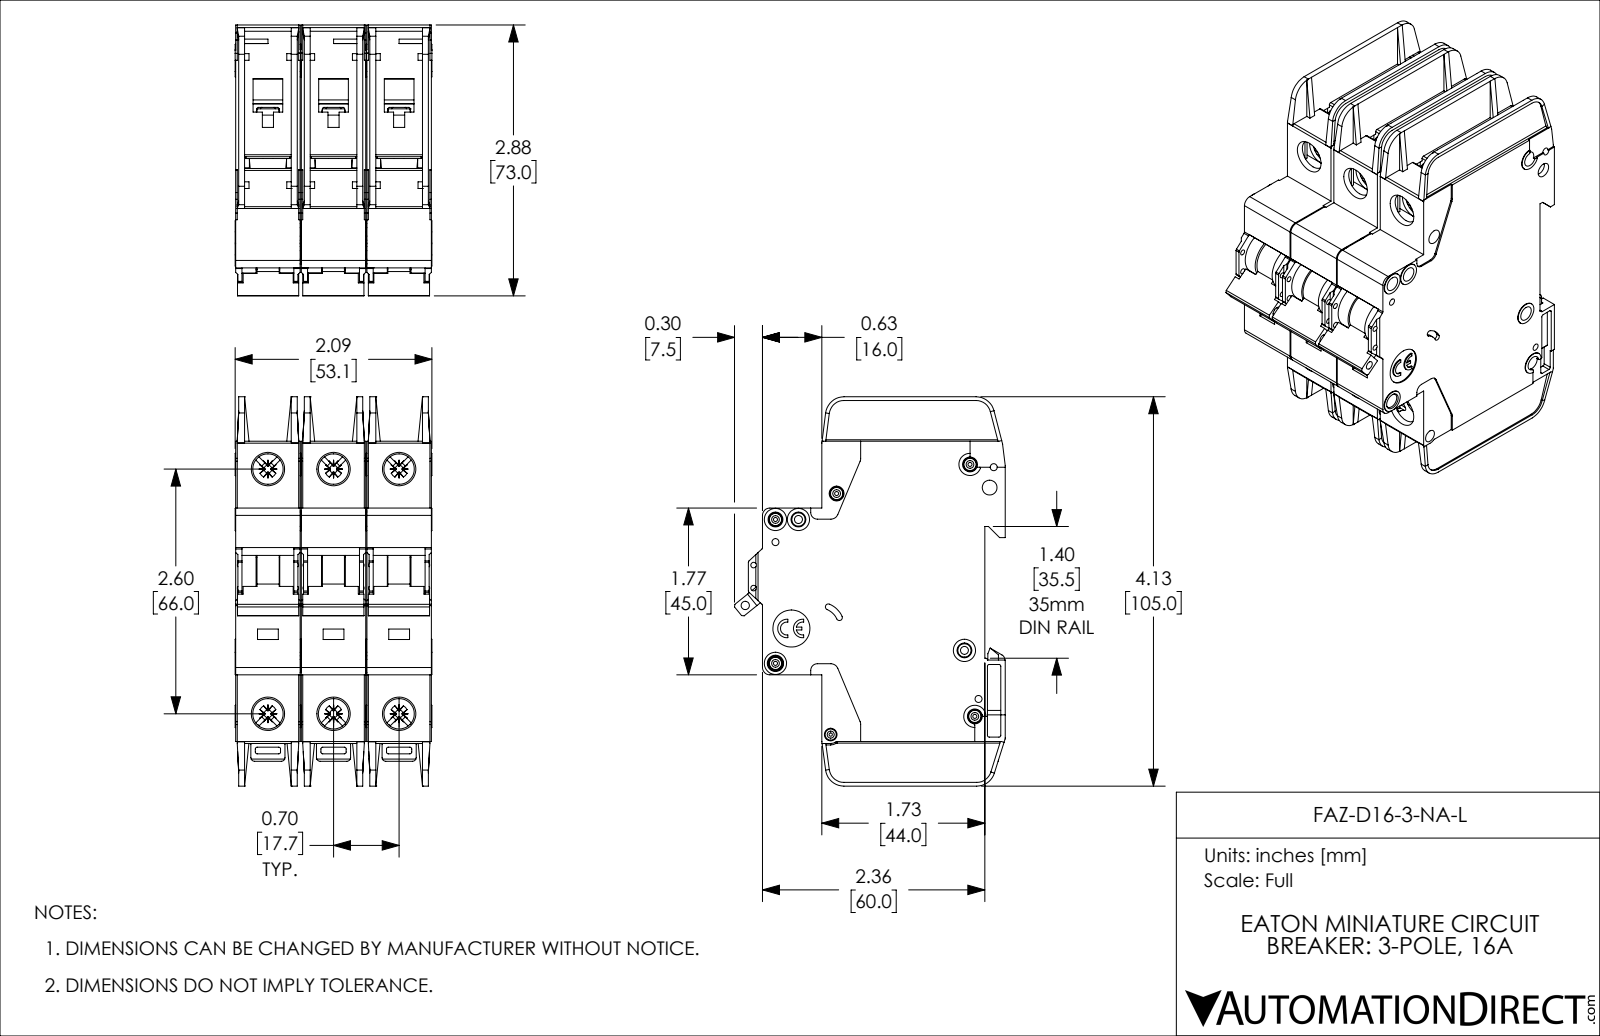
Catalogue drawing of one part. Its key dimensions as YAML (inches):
part_name: "FAZ-D16-3-NA-L"
step_written_by: "SolidWorks 2019 (AUTOMOTIVE_DESIGN)"
units: inches
bodies: {solids: 3, faces: 3381, planar: 2013, cylindrical: 1071, other: 297}
overall_size: [4.134, 2.876, 2.091]
volume: 14.05
surface_area: 123
round_holes:
  - {diameter: 0.157, count: 8}
  - {diameter: 0.323, count: 6}
  - {diameter: 0.043, count: 5}
  - {diameter: 0.075, count: 4}
  - {diameter: 0.059, count: 2}
  - {diameter: 0.085, count: 2}
  - {diameter: 0.035, count: 1}
  - {diameter: 0.089, count: 1}
  - {diameter: 0.098, count: 1}
  - {diameter: 0.134, count: 1}
  - {diameter: 0.394, count: 1}
round_bosses_or_shafts:
  - {diameter: 0.13, count: 5}
  - {diameter: 0.236, count: 4}
  - {diameter: 0.118, count: 4}
  - {diameter: 0.098, count: 3}
partial_cylinders:
  - {radius: 0.02, count: 72}
  - {radius: 0.016, count: 30}
  - {radius: 0.039, count: 18}
  - {radius: 0.043, count: 12}
  - {radius: 0.079, count: 12}
  - {radius: 0.008, count: 6}
  - {radius: 0.01, count: 6}
  - {radius: 0.028, count: 6}
face_to_face_distances: [0.697, 0.047, 1.394, 0.685, 0.591, 1.382, 0.744, 0.65, 0.106, 0.094]
hole_center_spacings: [0.697, 2.69, 2.598, 0.244, 0.537, 0.87, 1.394, 2.948]
